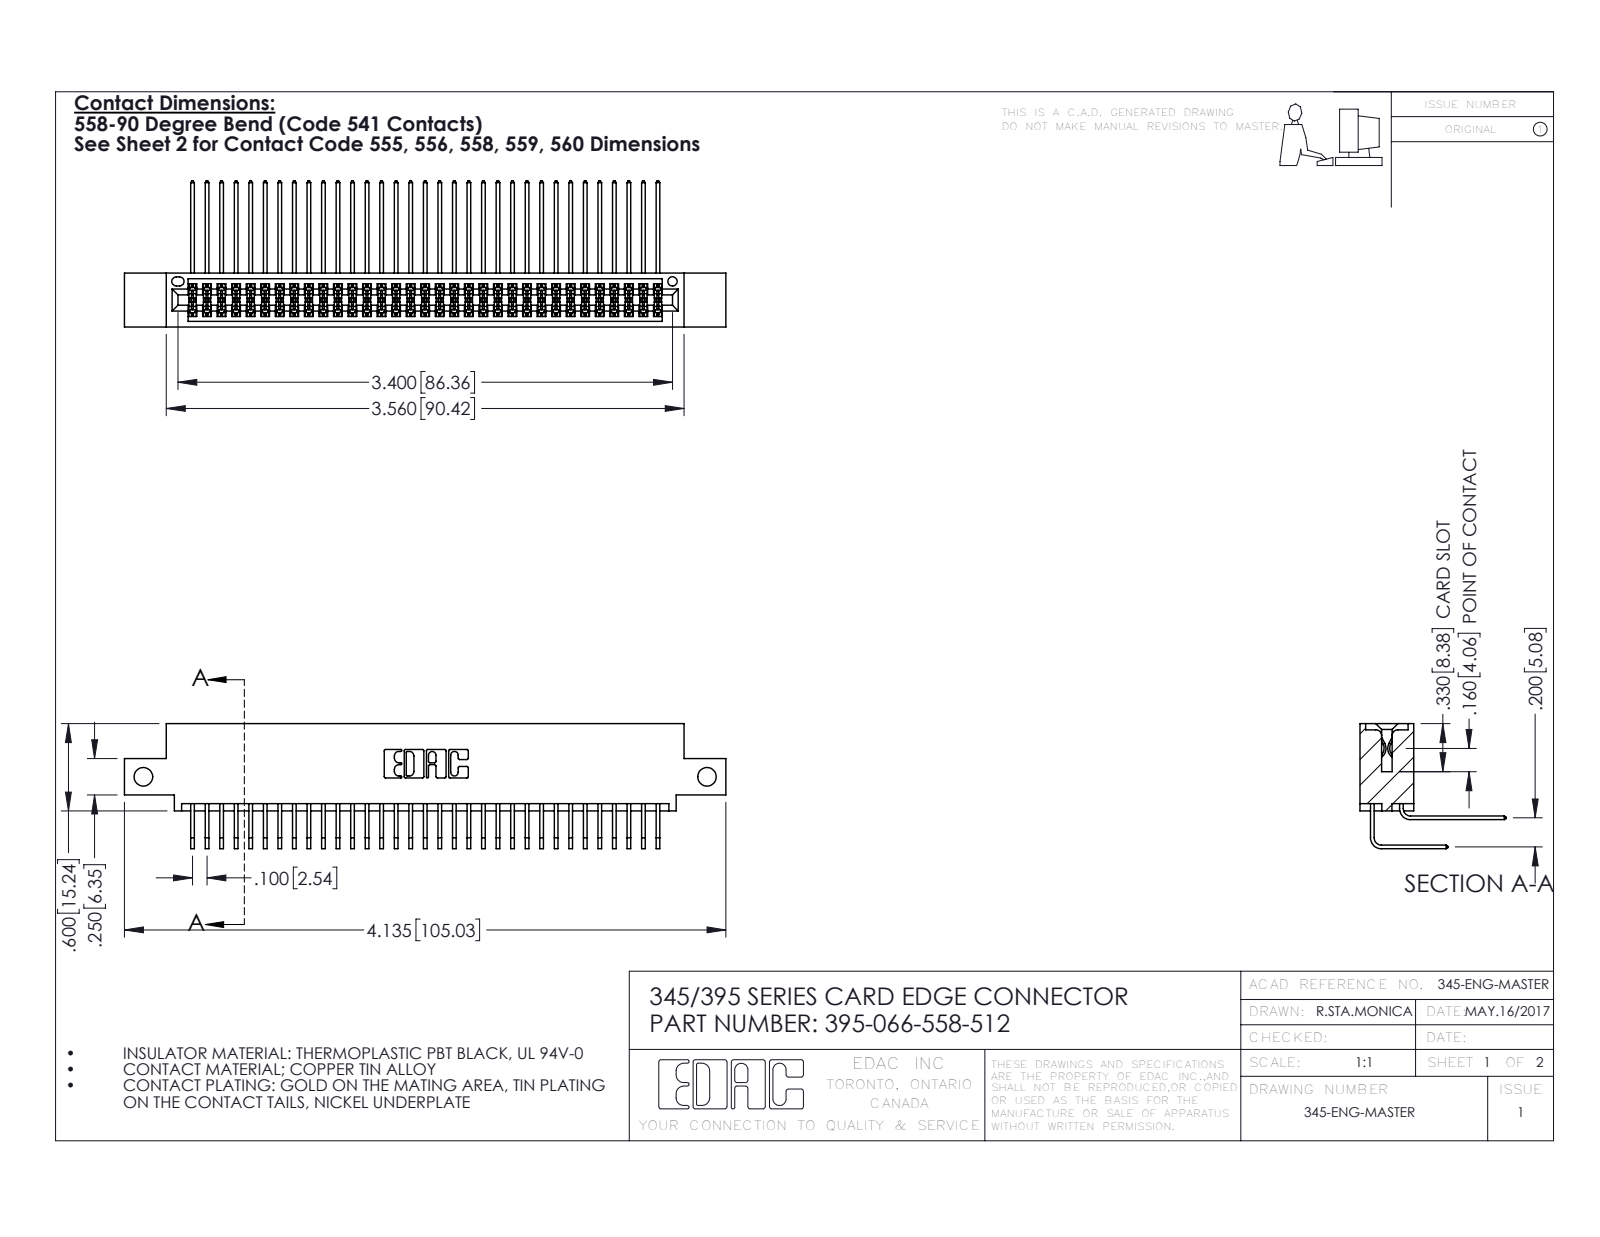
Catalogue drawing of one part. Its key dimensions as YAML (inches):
part_name: "345-292-001_558 Tail - 2; 395-066-558-512; 345-292-001_558 559 Tail - 1; 345 Part_0.110 Offset - Side Mount"
step_written_by: "SolidWorks 2016 (CONFIG_CONTROL_DESIGN)"
units: inches
bodies: {solids: 67, faces: 3562, planar: 2394, cylindrical: 1168, other: 0}
overall_size: [4.135, 1.005, 0.859]
volume: 0.631
surface_area: 26.13
round_holes:
  - {diameter: 0.128, count: 2}
  - {diameter: 0.064, count: 1}
partial_cylinders:
  - {radius: 0.006, count: 100}
  - {radius: 0.01, count: 22}
  - {radius: 0.007, count: 6}
  - {radius: 0.031, count: 6}
  - {radius: 0.026, count: 3}
  - {radius: 0.014, count: 2}
  - {radius: 0.019, count: 2}
  - {radius: 0.022, count: 2}
face_to_face_distances: [0.072, 0.298, 0.2, 0.37, 0.098, 0.272, 0.025, 0.225, 0.025, 0.175]
hole_center_spacings: [3.875]
